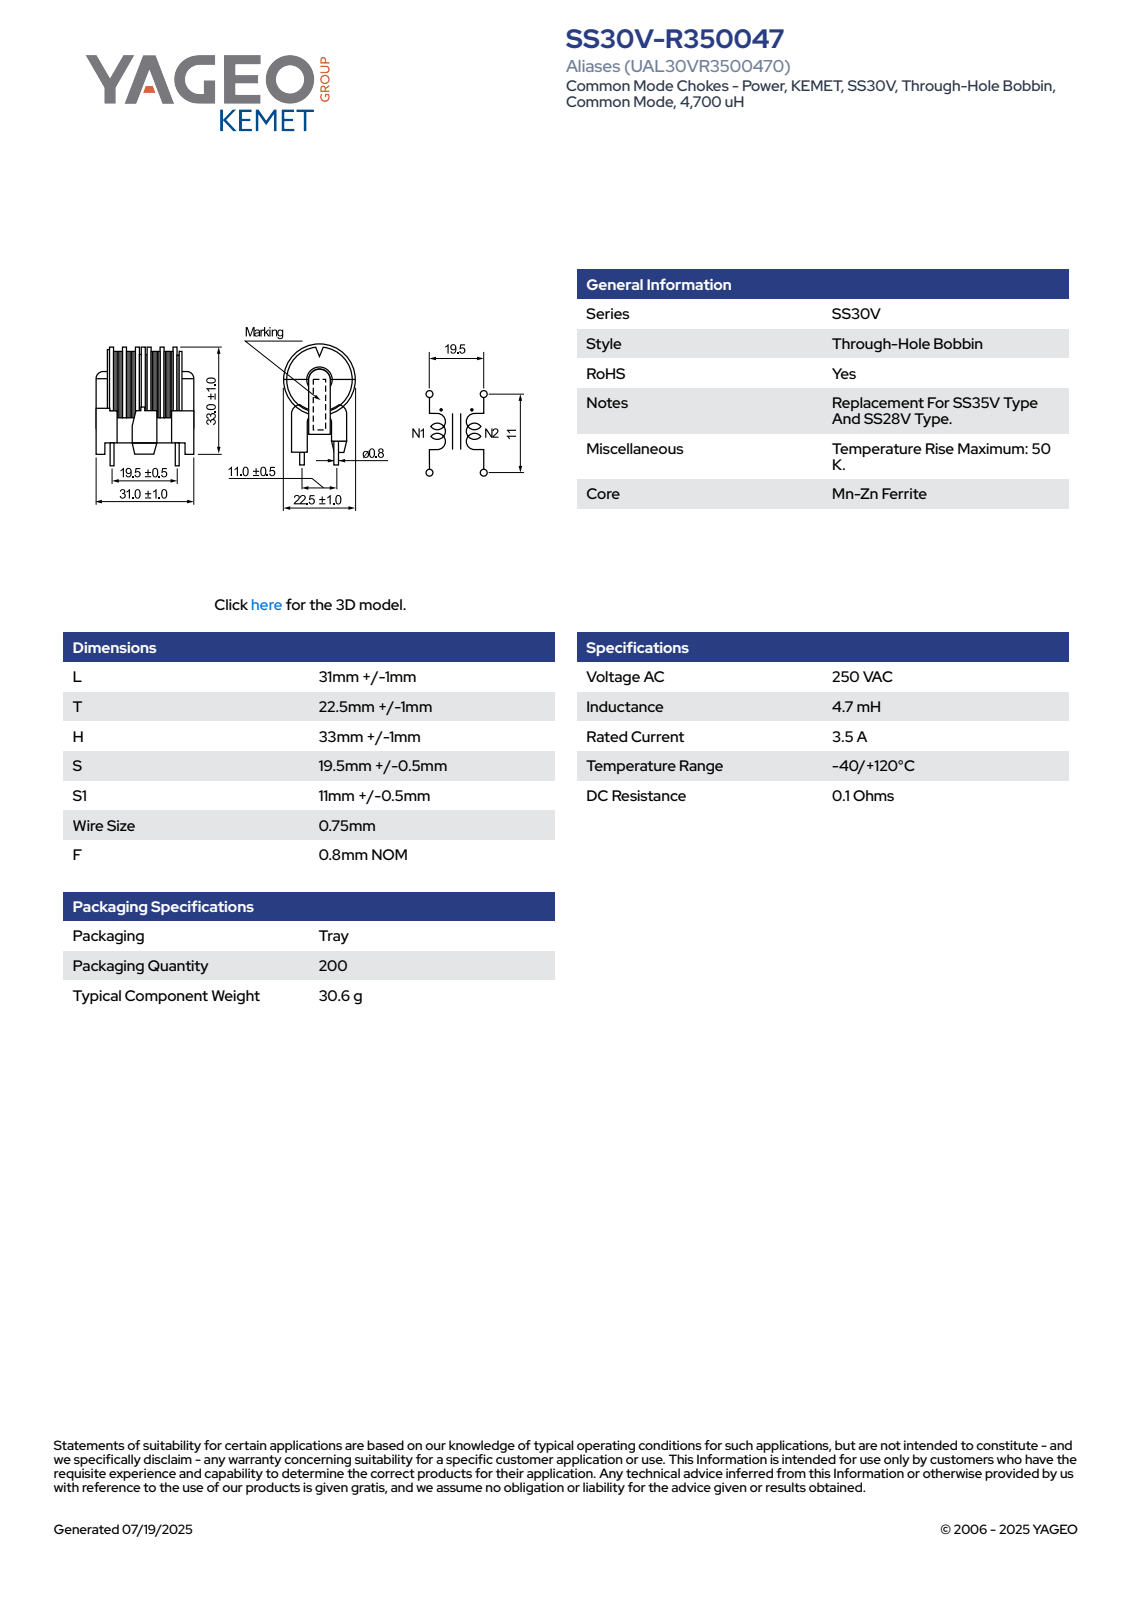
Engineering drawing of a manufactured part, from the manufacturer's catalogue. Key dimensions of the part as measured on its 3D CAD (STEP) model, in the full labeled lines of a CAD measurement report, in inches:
Part name (STEP PRODUCT): SS30V(MAX-LOGO)
STEP written by: SolidWorks 2018 (AUTOMOTIVE_DESIGN)
Units: inches
Bodies: 1 solid, 655 faces (265 planar, 203 cylindrical, 187 other)
Overall size (bounding box): 1.476 × 1.26 × 0.925
Volume: 0.654 in³ · Surface area: 14.11 in²
Round holes (diameter × count): ⌀0.287 ×1, ⌀0.303 ×1
Round bosses / shafts (diameter × count): ⌀0.031 ×4, ⌀0.925 ×1, ⌀0.85 ×1, ⌀0.789 ×1, ⌀0.654 ×1
Partial cylindrical surfaces — rounded edges, fillets, slot ends (radius × count): R0.02 ×43, R0.008 ×20, R0.016 ×16, R0.031 ×12, R0.039 ×11, R0.118 ×2, R0.183 ×1, R0.203 ×1
Main face-to-face distances: 0.444, 0.024, 0.071, 0.252, 0.274, 0.022, 0.467, 0.079, 0.047, 0.373
